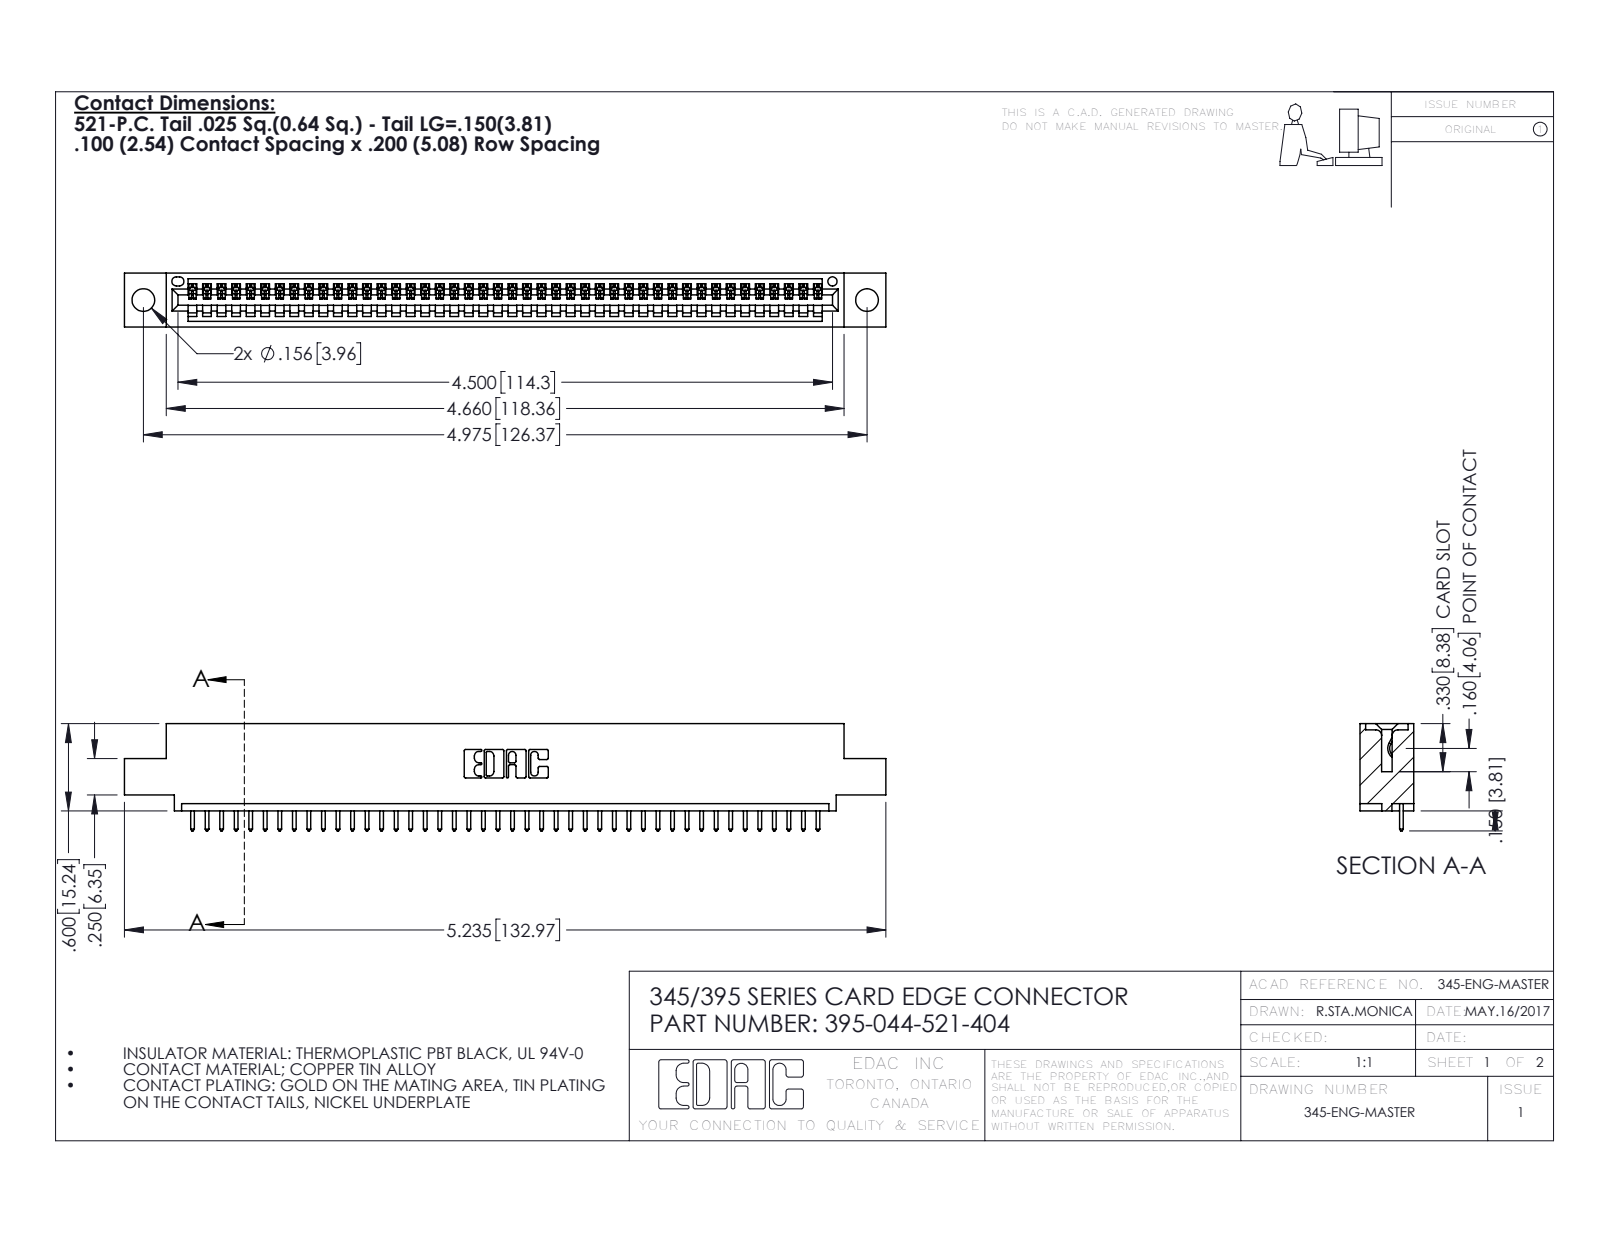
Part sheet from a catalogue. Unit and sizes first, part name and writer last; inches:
Units: inches
Overall size (bounding box): 5.235 × 0.737 × 0.37
Round holes (diameter × count): ⌀0.156 ×2, ⌀0.064 ×1
Partial cylindrical surfaces — rounded edges, fillets, slot ends (radius × count): R0.006 ×88, R0.01 ×88, R0.01 ×22, R0.007 ×6, R0.031 ×6, R0.026 ×3, R0.031 ×2, R0.04 ×2
Main face-to-face distances: 0.298, 0.072, 0.37, 0.2, 0.098, 0.272, 0.025, 0.225, 0.149, 0.072
Hole centre spacings: 0.27, 4.739, 4.975
Volume: 0.754 in³ · Surface area: 24.57 in²
Bodies: 45 solids, 2682 faces (1844 planar, 838 cylindrical, 0 other)
Part name (STEP PRODUCT): 345-292-001_345-293-121; 345 Part_0.110 Offset - 0.156 Dia-TH; 395-044-521-404
STEP written by: SolidWorks 2016 (CONFIG_CONTROL_DESIGN)
